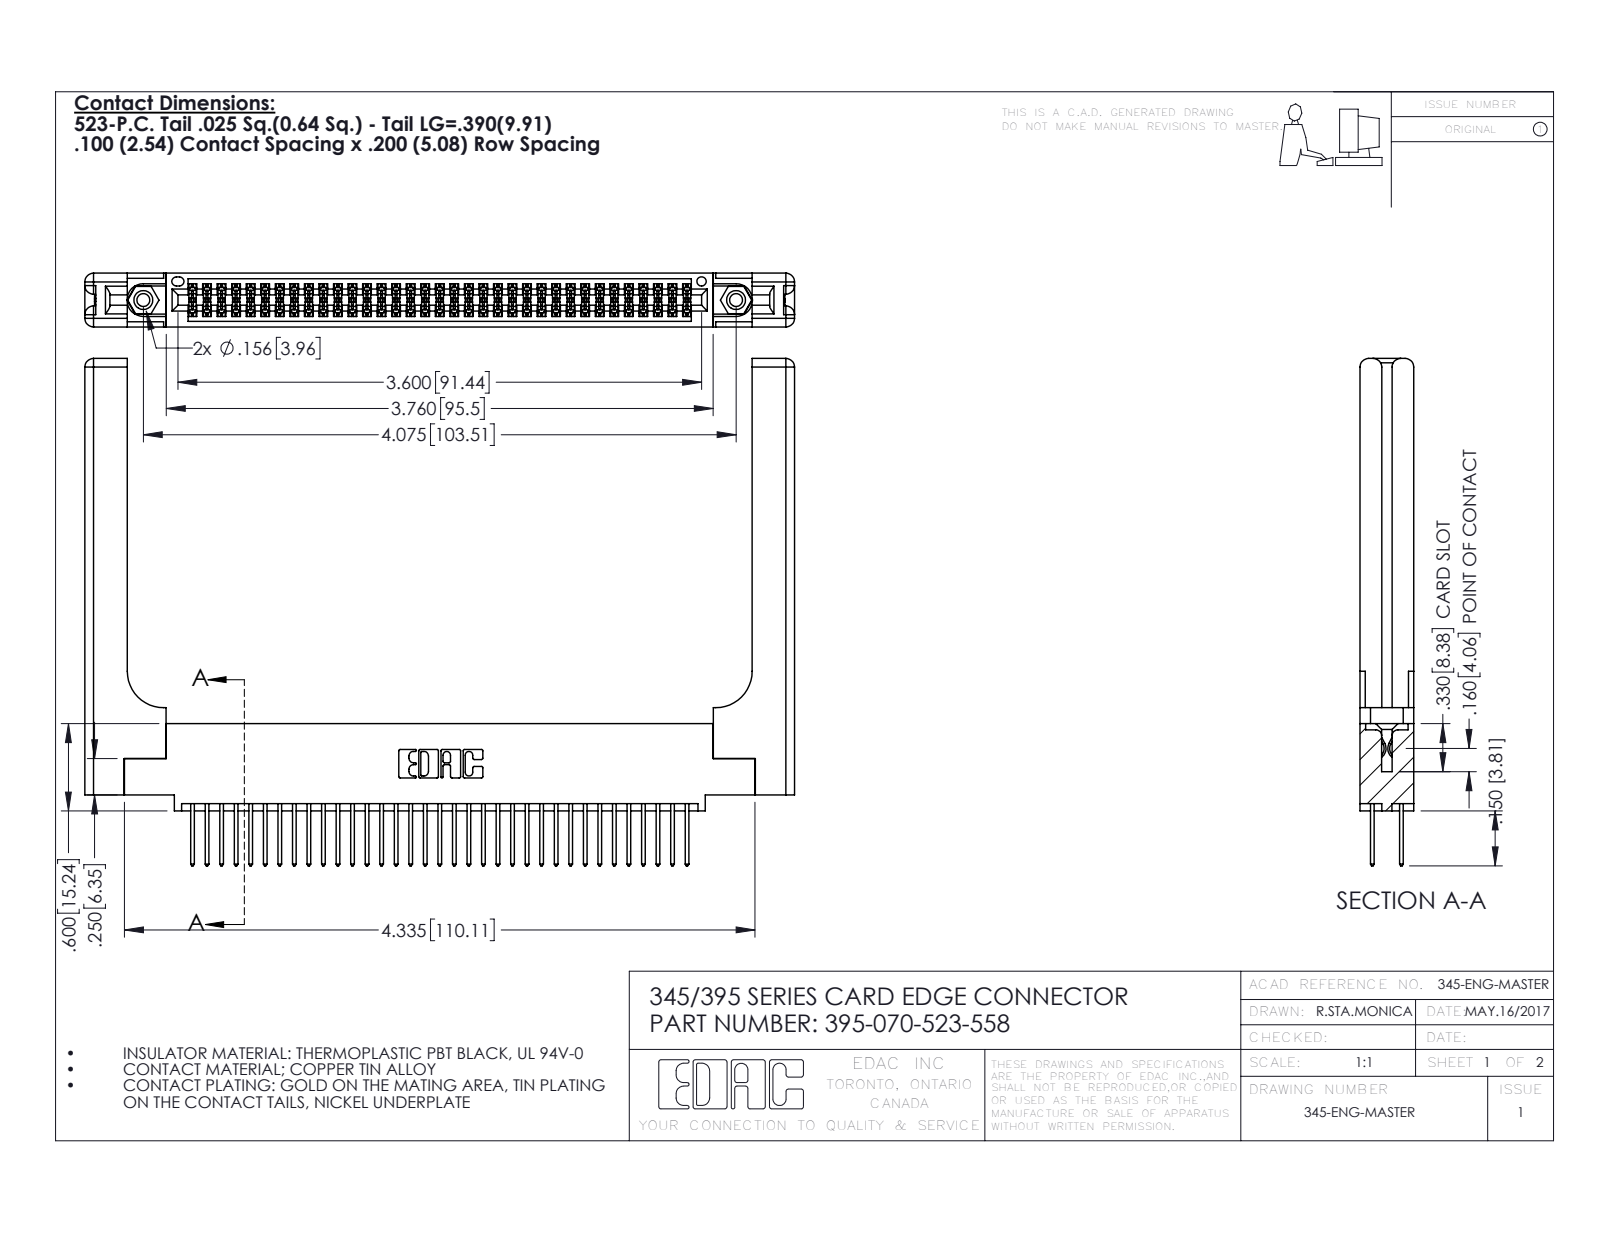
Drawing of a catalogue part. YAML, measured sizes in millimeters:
part_name: "345-250-001_345-250-001-102; 345-292-001_345-293-123; 395-070-523-558; 345 Part_0.110 Offset - 0.156 Dia-TH (+1 more)"
step_written_by: "SolidWorks 2016 (CONFIG_CONTROL_DESIGN)"
units: millimeters
bodies: {solids: 75, faces: 3886, planar: 2542, cylindrical: 1284, other: 60}
overall_size: [123.9, 88.6, 9.4]
volume: 20520
surface_area: 23460
round_holes:
  - {diameter: 2.3, count: 2}
  - {diameter: 3.2, count: 2}
  - {diameter: 4, count: 2}
  - {diameter: 1.6, count: 1}
round_bosses_or_shafts:
  - {diameter: 3.9, count: 2}
partial_cylinders:
  - {radius: 0.2, count: 105}
  - {radius: 0.3, count: 70}
  - {radius: 0.3, count: 22}
  - {radius: 1.5, count: 16}
  - {radius: 0.2, count: 6}
  - {radius: 0.8, count: 6}
  - {radius: 0.7, count: 3}
  - {radius: 0.4, count: 2}
face_to_face_distances: [1.8, 7.6, 9.4, 2.5, 6.9, 0.6, 5.1, 5.7, 3.8, 3.8]
hole_center_spacings: [6.9, 97.5, 103.5]
